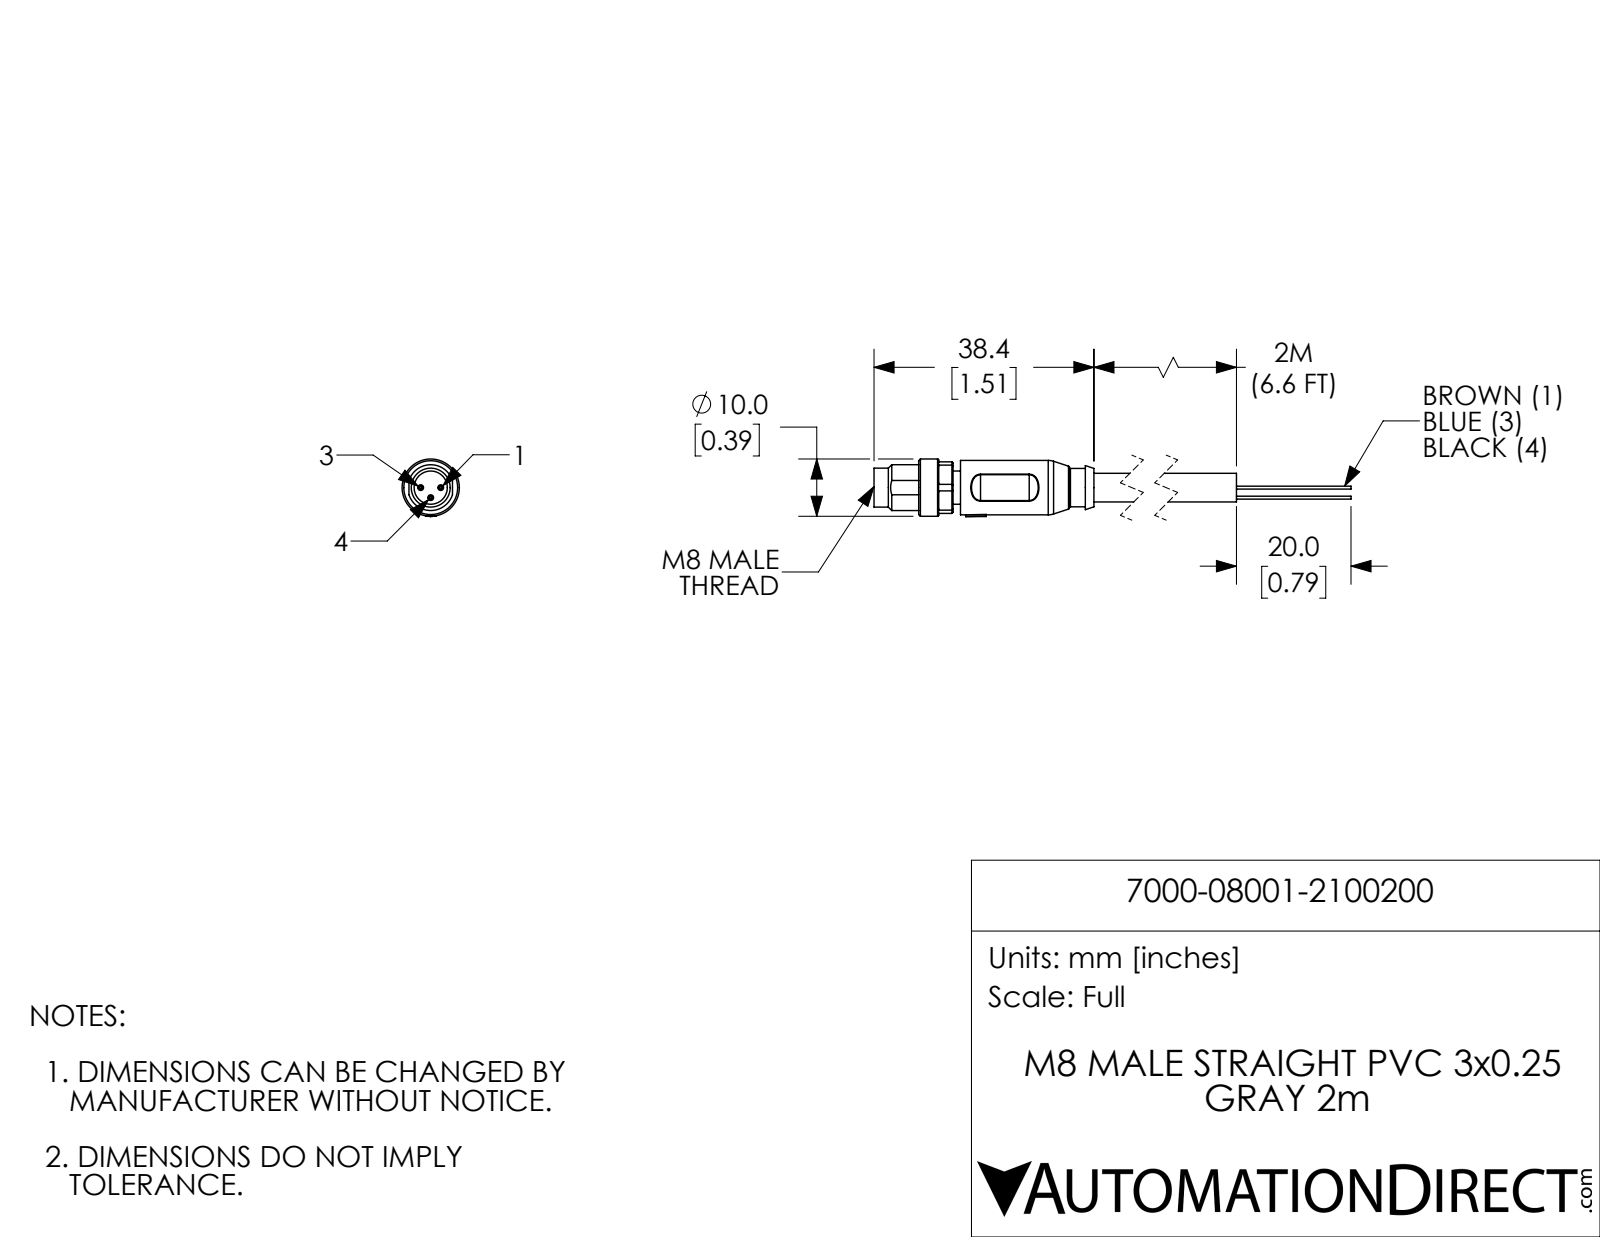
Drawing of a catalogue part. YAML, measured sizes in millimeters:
part_name: "7000-08001-2100200"
step_written_by: "SolidWorks 2017 (AUTOMOTIVE_DESIGN)"
units: millimeters
bodies: {solids: 4, faces: 119, planar: 41, cylindrical: 44, other: 34}
overall_size: [78.4, 10.05, 10]
volume: 2535
surface_area: 1801
round_holes:
  - {diameter: 5.8, count: 1}
round_bosses_or_shafts:
  - {diameter: 1, count: 3}
  - {diameter: 0.51, count: 3}
  - {diameter: 10, count: 1}
  - {diameter: 9.5, count: 1}
  - {diameter: 8, count: 1}
  - {diameter: 6.8, count: 1}
  - {diameter: 6.7, count: 1}
  - {diameter: 5, count: 1}
partial_cylinders:
  - {radius: 0.2, count: 4}
  - {radius: 2.5, count: 4}
  - {radius: 4.9, count: 1}
  - {radius: 5.05, count: 1}
face_to_face_distances: [8.3, 1.3, 9, 0.35, 7.95, 8.8, 10.1, 53.4, 44.6, 43.3]
